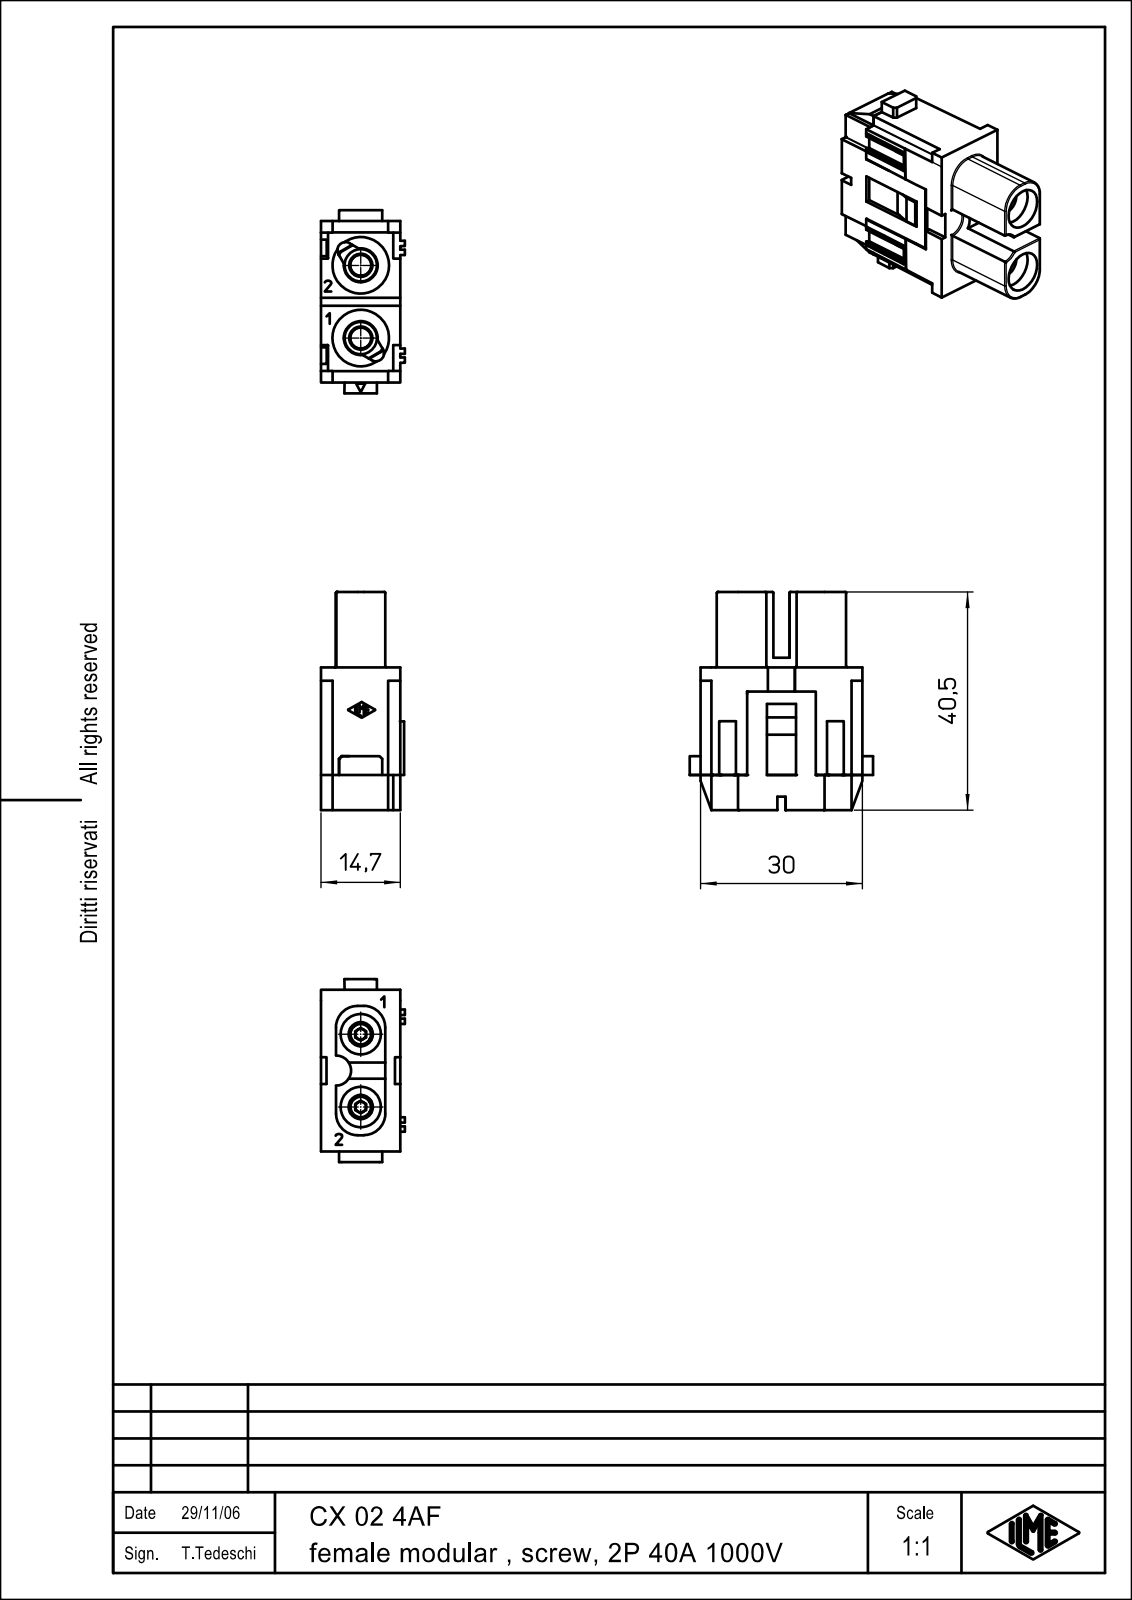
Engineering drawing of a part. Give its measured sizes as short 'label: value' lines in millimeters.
name: CX_02_4AF
written by: CoCreate Modeling 16.00A 16-Aug-2008 (C) Parametric Technology GmbH (AUTOMOTIVE_DESIGN)
unit: mm
bodies: 1 solid, 580 faces (400 planar, 88 cylindrical, 92 other)
size: 40.5 × 34 × 15.6
volume: 10 849 mm³; area: 7 086 mm²
holes: 2× ⌀2, 2× ⌀4, 2× ⌀4.2, 2× ⌀4.5, 2× ⌀6, 2× ⌀7.5, 2× ⌀10.5
bosses: 2× ⌀4.4
rounds: 10× R0.2, 5× R0.1, 4× R0.5, 4× R4, 2× R1, 2× R1.5, 2× R2.52, 2× R3.15
face distances: 14.7, 1, 2.25, 2.77, 11.93, 2, 6.5, 9.48, 11.45, 30
hole spacings: 13.5
